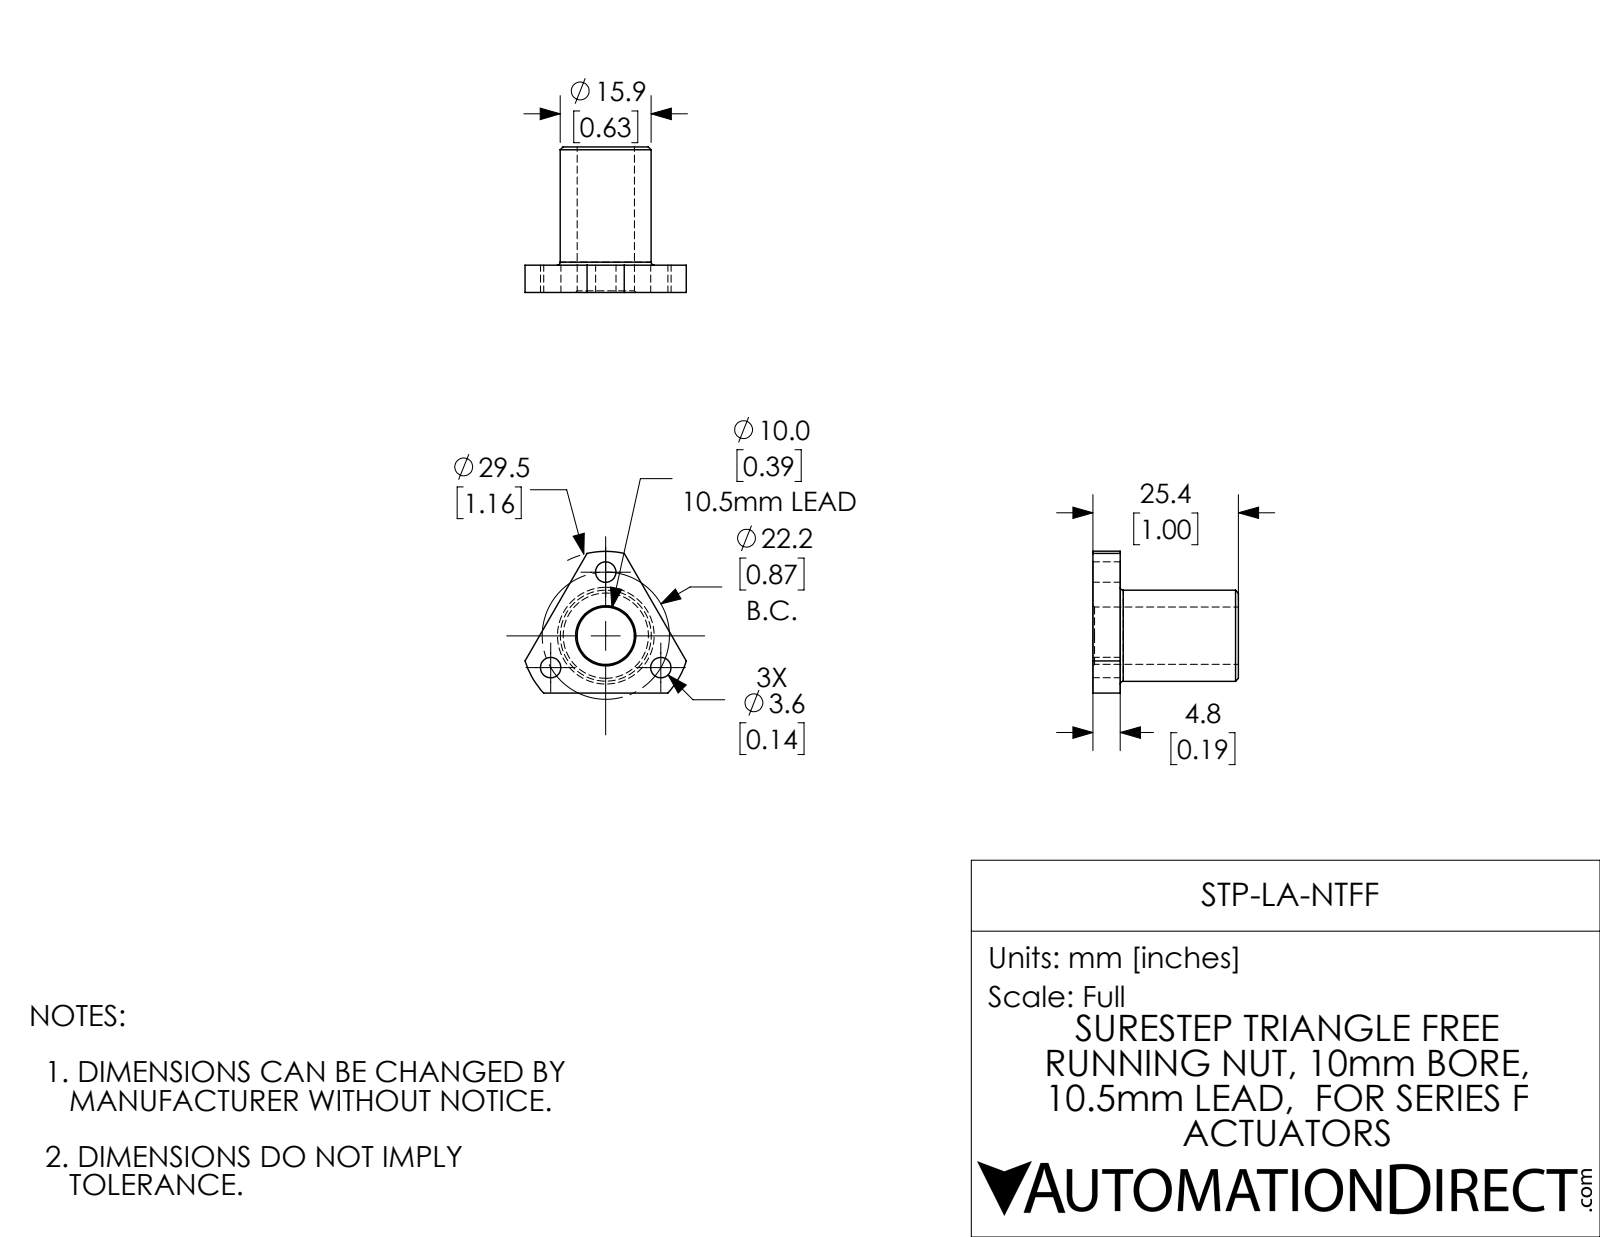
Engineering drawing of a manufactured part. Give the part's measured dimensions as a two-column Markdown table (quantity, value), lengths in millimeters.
| quantity | value |
| --- | --- |
| part name | STP-LA-NTFF |
| STEP written by | SolidWorks 2017 (AUTOMOTIVE_DESIGN) |
| units | millimeters |
| bodies | 1 solid, 25 faces (6 planar, 13 cylindrical, 6 other) |
| overall size | 28.16 × 25.4 × 24.75 |
| volume | 4 183 mm³ |
| surface area | 3 083 mm² |
| round holes (diameter × count) | 3.56 × 3, 10 × 1 |
| round bosses / shafts (diameter × count) | 15.88 × 1 |
| partial cylindrical surfaces (radius × count) | 14.75 × 1 |
| main face-to-face distances | 4.76, 20.64, 25.4 |
| hole center spacings | 11.11, 19.24, 19.25 |
